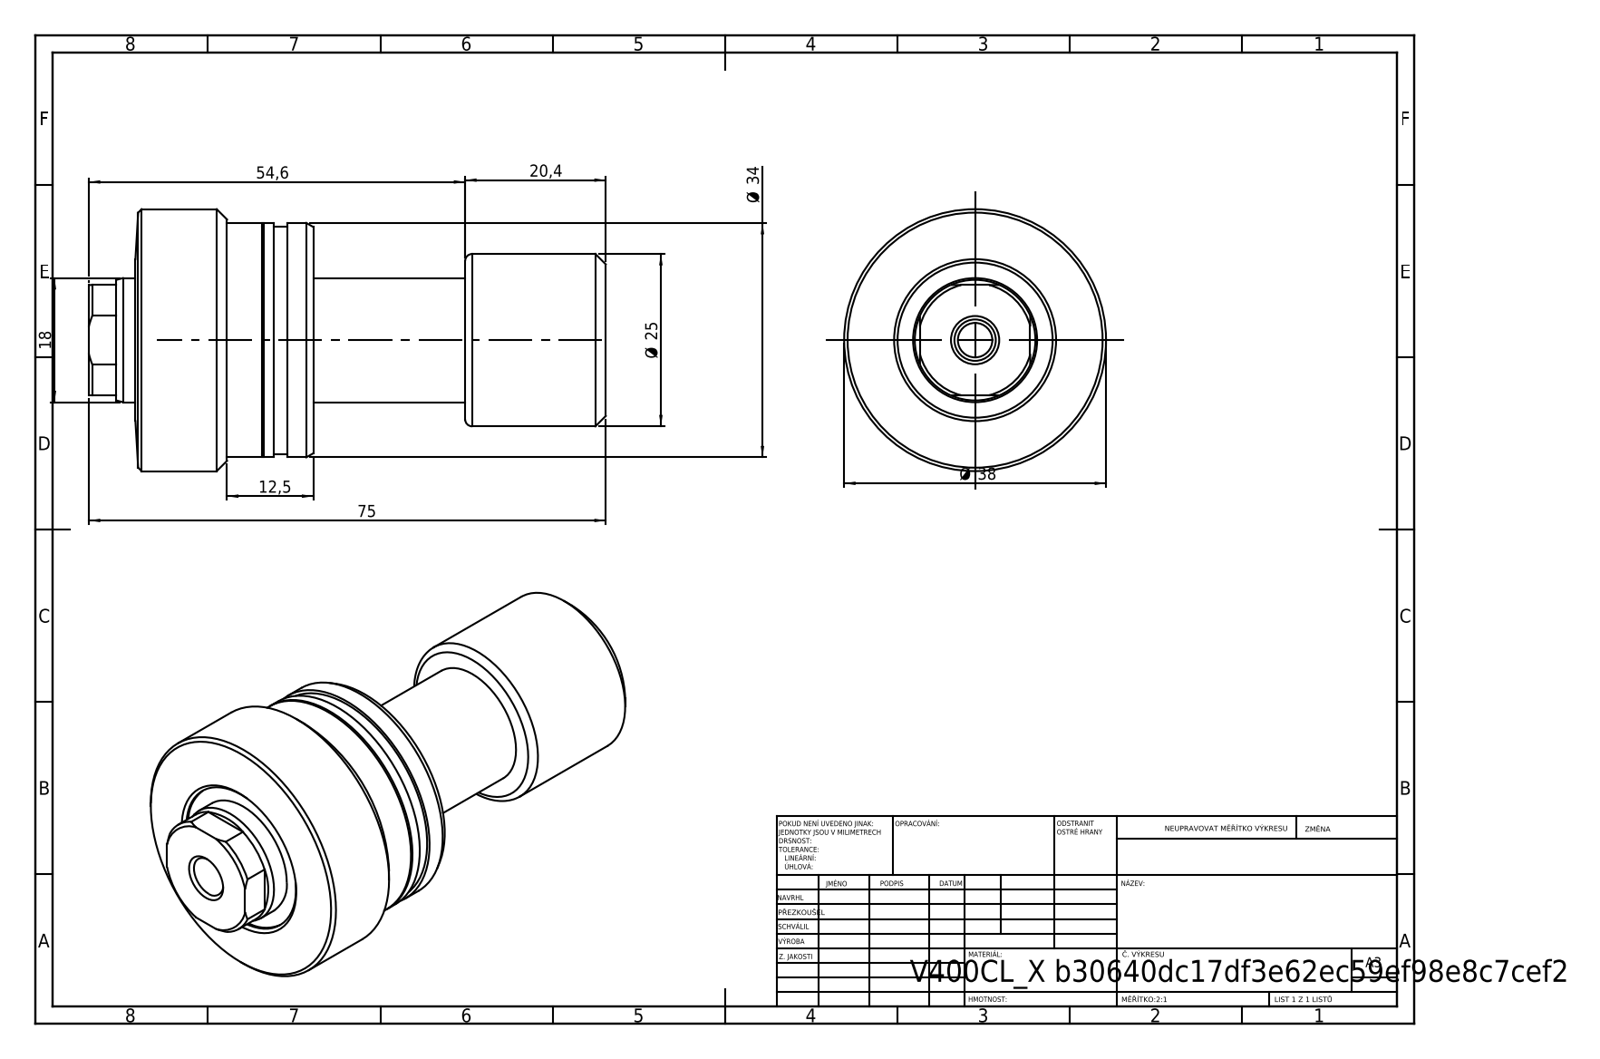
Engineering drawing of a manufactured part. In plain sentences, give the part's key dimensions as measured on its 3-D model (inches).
The part is named "V400CL_PC_X; V400CL_VC_X". Its 3-D file was written by "SolidWorks 2019 (CONFIG_CONTROL_DESIGN)". It is 2 solids with 79 faces: 19 planar, 30 cylindrical and 30 other. Overall it measures 2.953 by 1.496 by 1.496 inches. Its volume is 2.585 cubic inches and its surface area 18.61 square inches. Round holes: 1 of diameter 0.081, 1 of diameter 0.197, 1 of diameter 0.236, 1 of diameter 0.709, 1 of diameter 0.886. Round bosses or shafts: 1 of diameter 1.496, 1 of diameter 1.339, 1 of diameter 1.299, 1 of diameter 0.984. Partial cylindrical surfaces (rounded edges, fillets, slot ends): 1 of radius 0.344. The main face-to-face distances are 1.671, 2.953, 1.281, 0.803, 0.868, 2.15, 2.656, 1.852, 0.984, 0.297.
